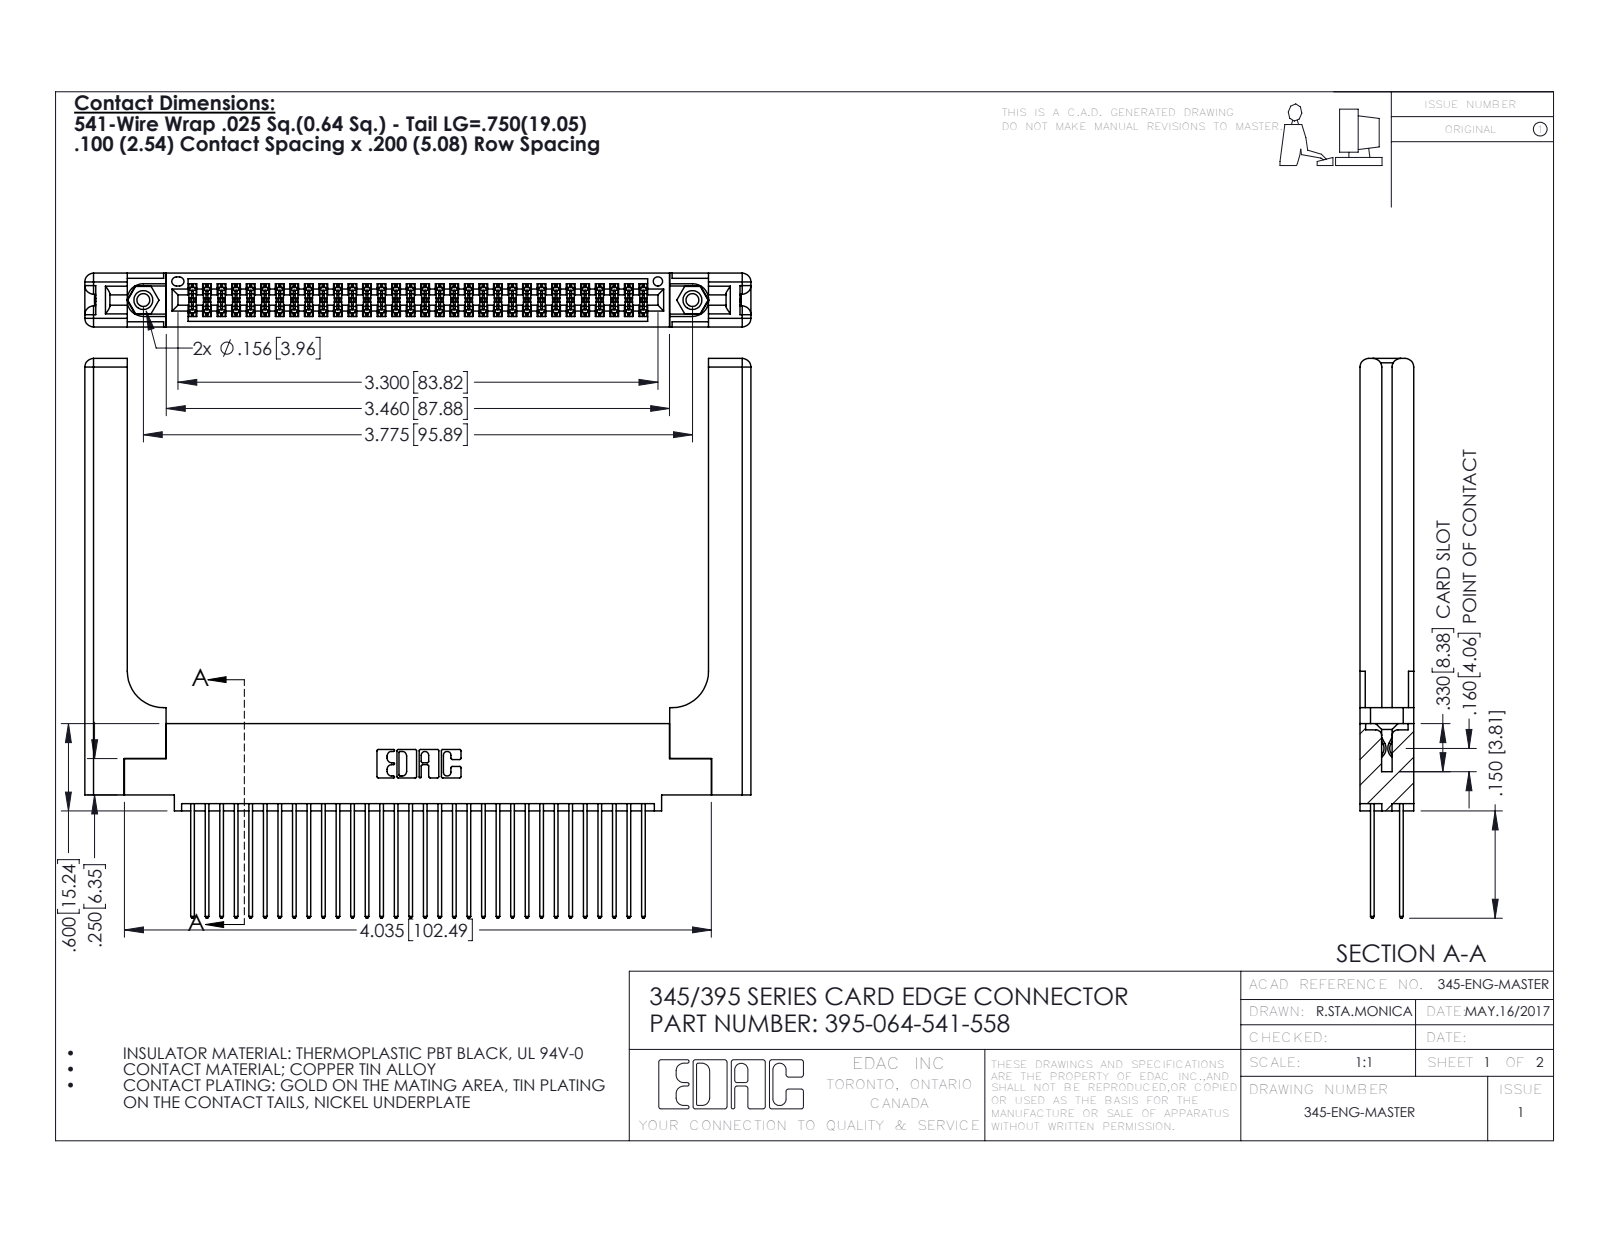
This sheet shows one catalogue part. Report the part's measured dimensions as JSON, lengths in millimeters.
{"part_name": "345-292-001_345-293-141; 395-064-541-558; 345-220-058_345-220-058; 345-250-001_345-250-001-102 (+1 more)", "step_written_by": "SolidWorks 2016 (CONFIG_CONTROL_DESIGN)", "units": "millimeters", "bodies": {"solids": 69, "faces": 3586, "planar": 2344, "cylindrical": 1182, "other": 60}, "overall_size": [116.3, 97.7, 9.4], "volume_mm3": 19980, "surface_area_mm2": 23680, "round_holes": [[2.3, 2], [3.2, 2], [4, 2], [1.6, 1]], "round_bosses_or_shafts": [[3.9, 2]], "partial_cylinders_radius": [[0.2, 96], [0.3, 64], [0.3, 22], [1.5, 16], [0.2, 6], [0.8, 6], [0.7, 3], [0.4, 2]], "face_to_face_distances": [1.8, 7.6, 9.4, 2.5, 6.9, 0.6, 5.1, 5.7, 4.4, 3.8], "hole_center_spacings": [6.9, 89.9, 95.9]}
